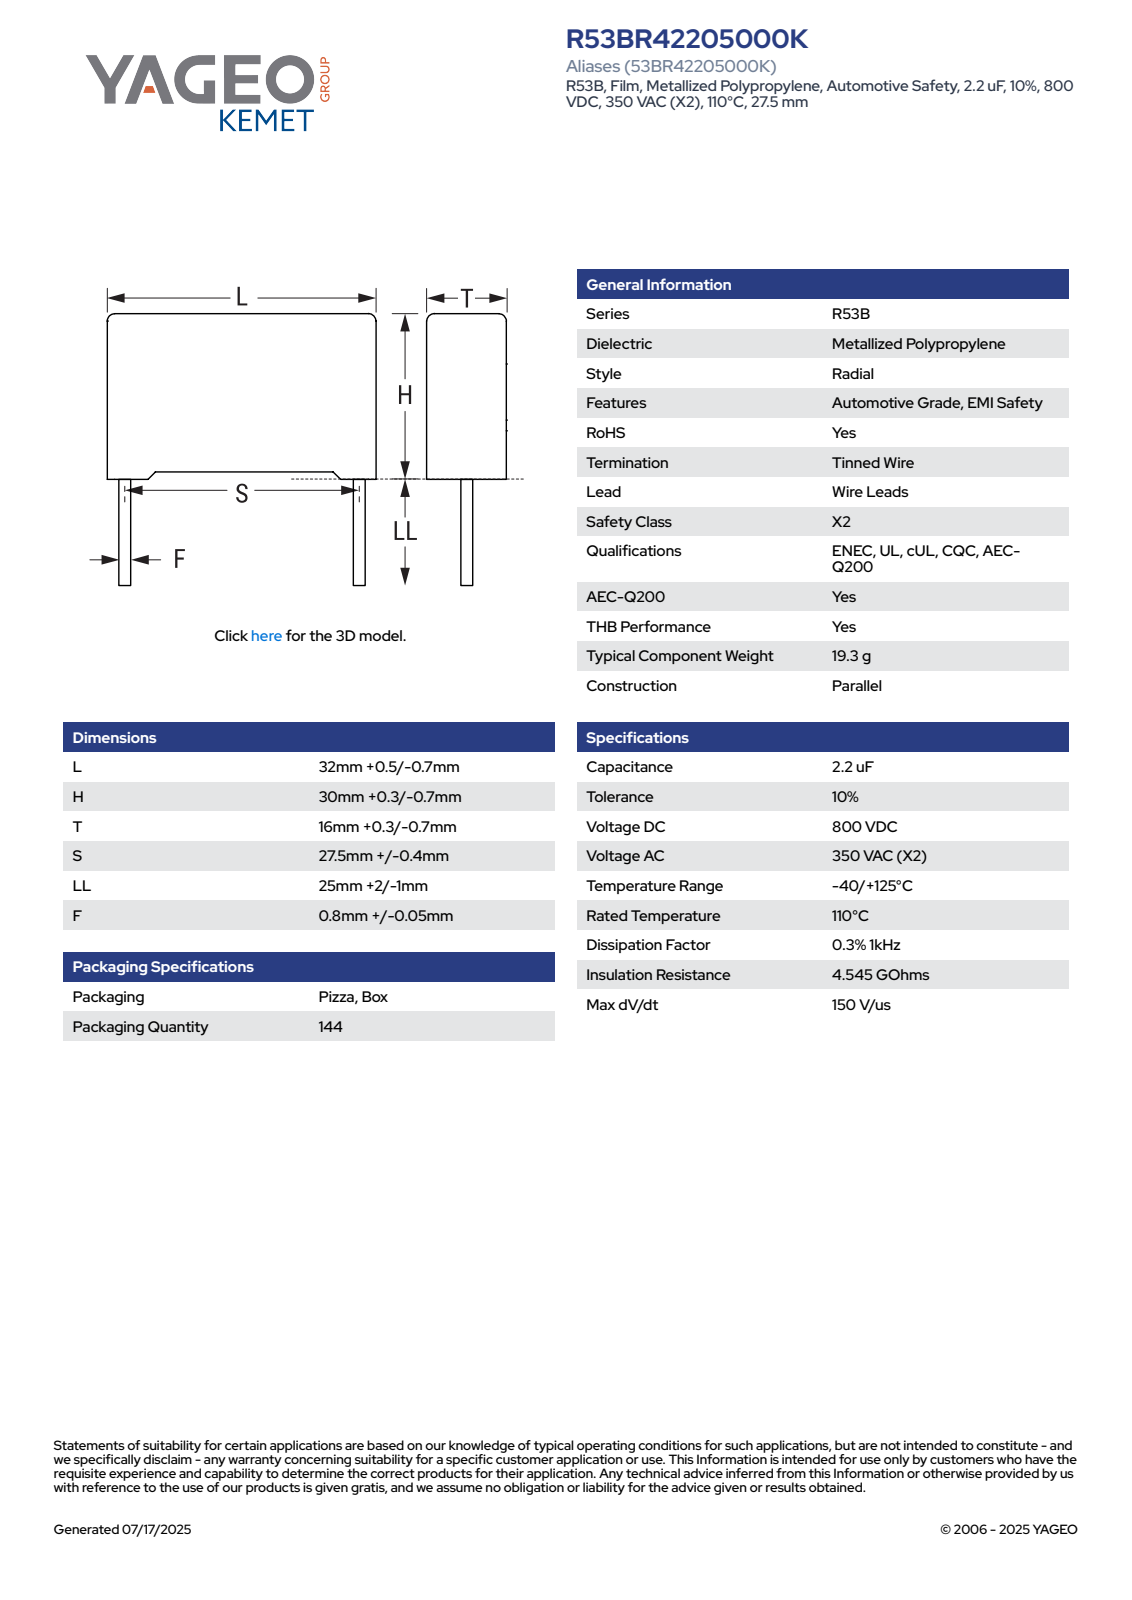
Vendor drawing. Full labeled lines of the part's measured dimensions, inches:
Part name (STEP PRODUCT): CFR_RB2_32X30X16_L32.5H30.3T16.3S27.5LL27F0.85
STEP written by: SolidWorks 2021 (AUTOMOTIVE_DESIGN)
Units: inches
Bodies: 4 solids, 85 faces (77 planar, 8 cylindrical, 0 other)
Overall size (bounding box): 2.256 × 1.28 × 0.642
Volume: 0.952 in³ · Surface area: 6.527 in²
Round bosses / shafts (diameter × count): ⌀0.033 ×2
Partial cylindrical surfaces — rounded edges, fillets, slot ends (radius × count): R0.02 ×4
Main face-to-face distances: 0.642, 1.28, 1.152, 1.163, 0.03, 0.041, 1.193, 0.043, 1.237, 0.642
